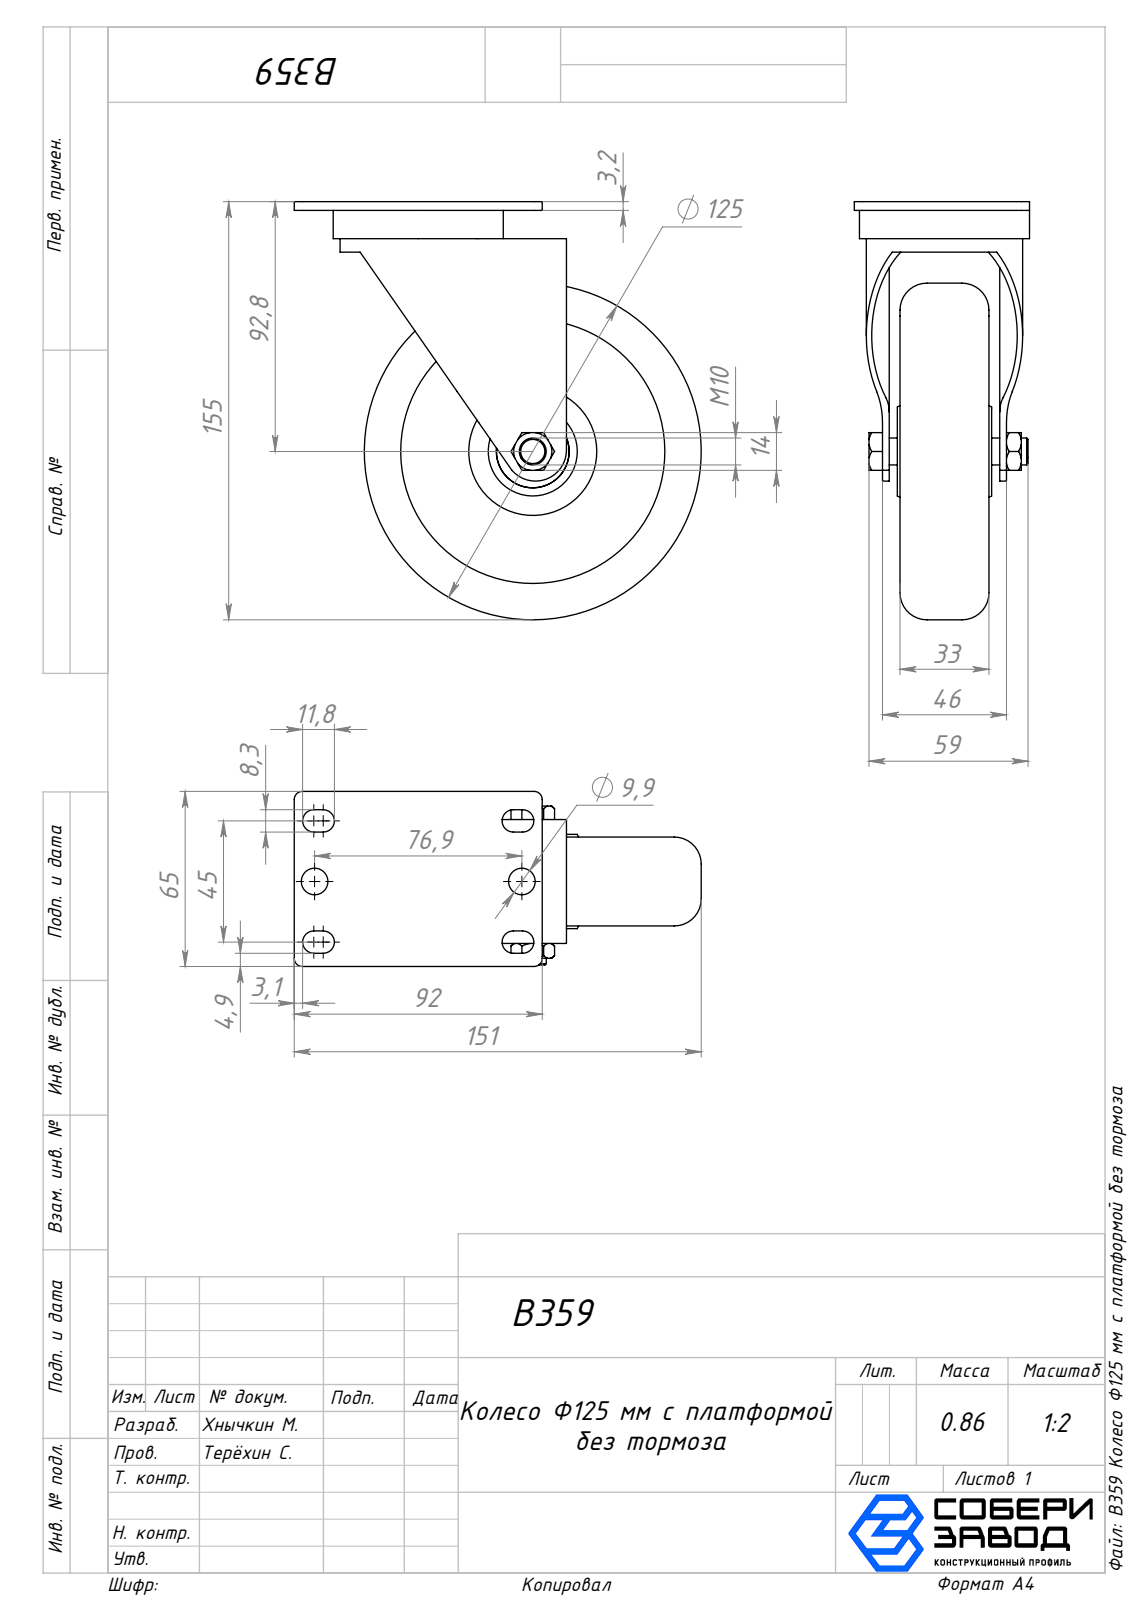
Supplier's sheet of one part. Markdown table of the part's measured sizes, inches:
| quantity | value |
| --- | --- |
| part name | B359 пластина_00; B359 Болт_с резьбой; 359 стойка_00; B359 внутрь колеса_00 (+4 more) |
| STEP written by | SolidWorks 2025 (AUTOMOTIVE_DESIGN) |
| units | inches |
| bodies | 7 solids, 346 faces (58 planar, 118 cylindrical, 170 other) |
| overall size | 6.112 × 5.944 × 2.559 |
| volume | 19.36 in³ |
| surface area | 152.1 in² |
| round holes (diameter × count) | 0.39 × 2, 0.354 × 1, 0.709 × 1, 1.063 × 1, 2.021 × 1, 2.139 × 1, 2.406 × 1 |
| round bosses / shafts (diameter × count) | 4.921 × 1, 2.484 × 1, 2.176 × 1, 2.126 × 1, 1.89 × 1, 0.394 × 1 |
| partial cylindrical surfaces (radius × count) | 0.163 × 8, 0.118 × 4, 0.197 × 2, 0.236 × 2, 0.63 × 2, 0.453 × 1, 1.142 × 1 |
| main face-to-face distances | 0.728, 0.098, 0.128, 1.713, 0.413, 0.827, 0.984, 0.886, 0.541, 0.157 |
| hole center spacings | 1.514, 3.028 |
